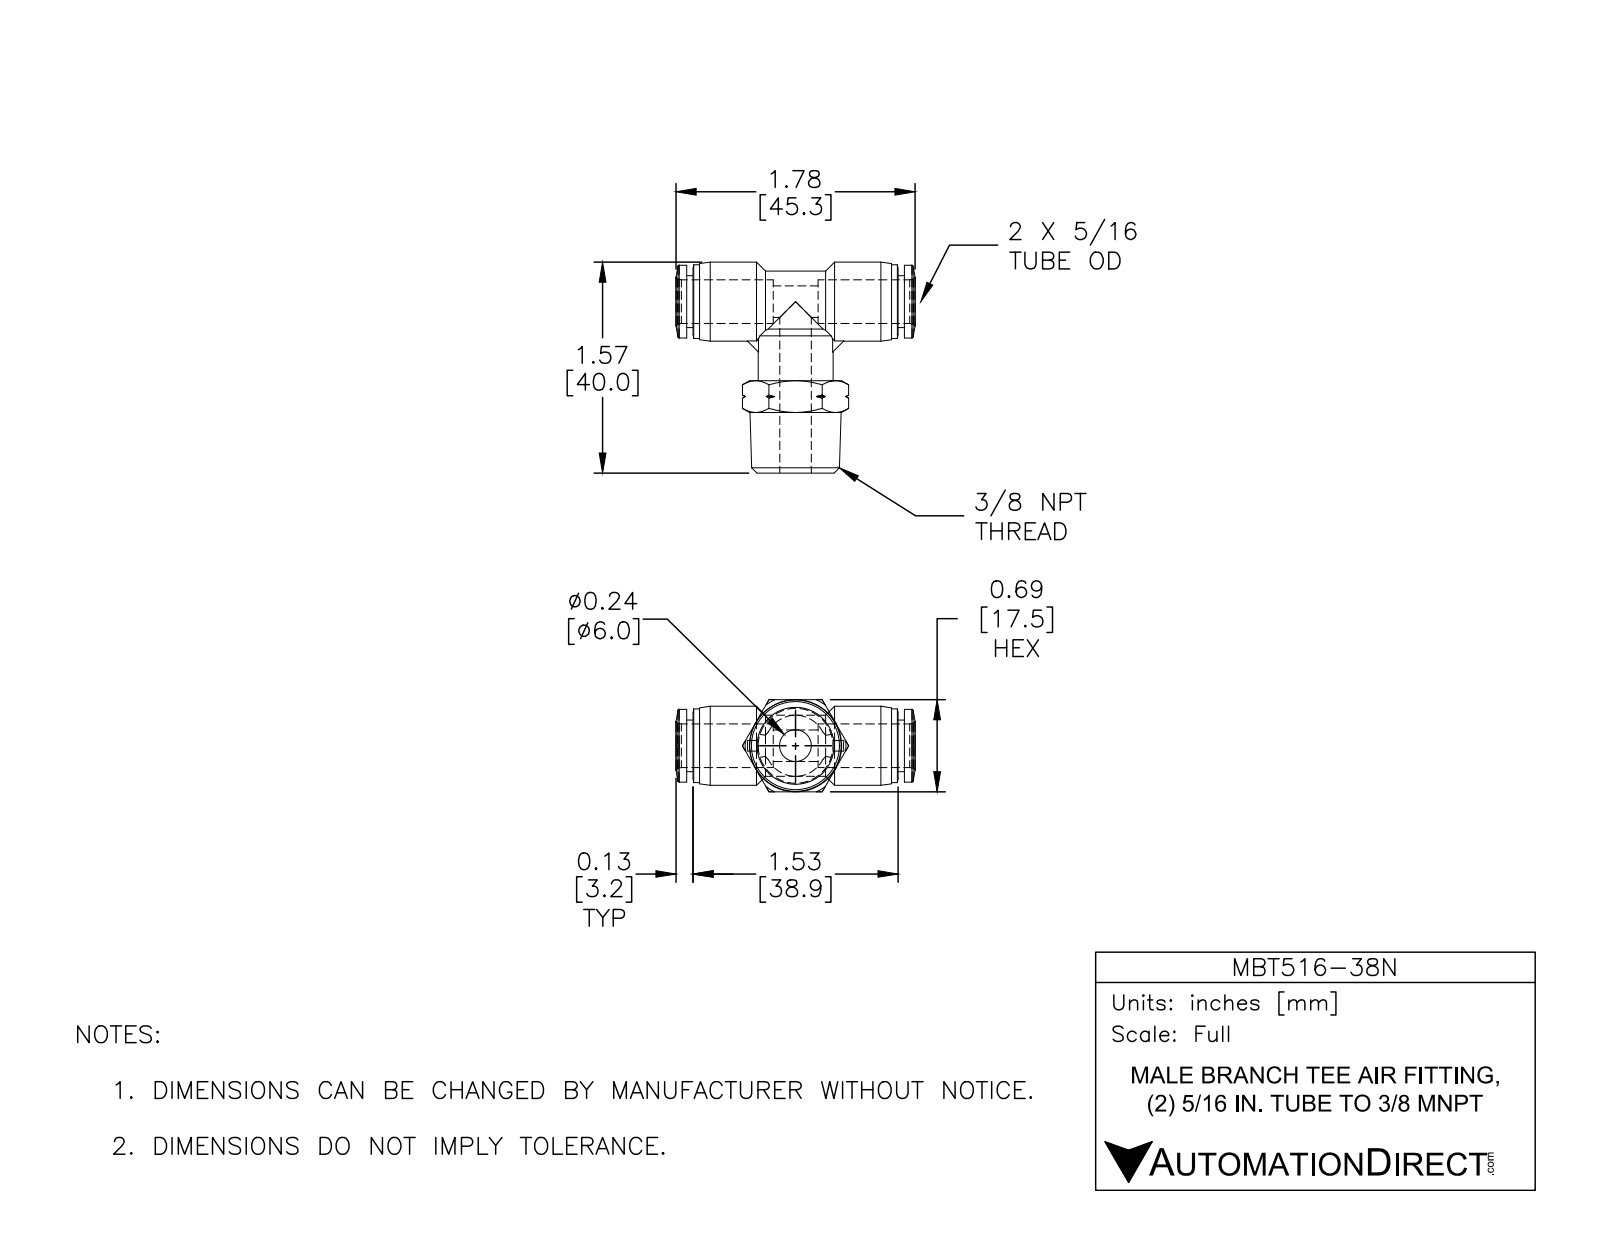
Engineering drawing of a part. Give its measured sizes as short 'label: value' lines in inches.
name: MBT516-38N
written by: SolidWorks 2015 (CONFIG_CONTROL_DESIGN)
unit: in
bodies: 1 solid, 122 faces (23 planar, 34 cylindrical, 65 other)
size: 1.783 × 1.575 × 0.687
volume: 0.561 in³; area: 8.905 in²
holes: 2× ⌀0.236, 1× ⌀0.327
bosses: 1× ⌀0.591, 1× ⌀0.559, 1× ⌀0.551, 1× ⌀0.543, 1× ⌀0.457, 1× ⌀0.386
rounds: 1× R0.228
face distances: 0.687, 0.047, 1.579, 0.689, 1.626, 0.646, 0.98, 0.598, 0.933, 1.531
